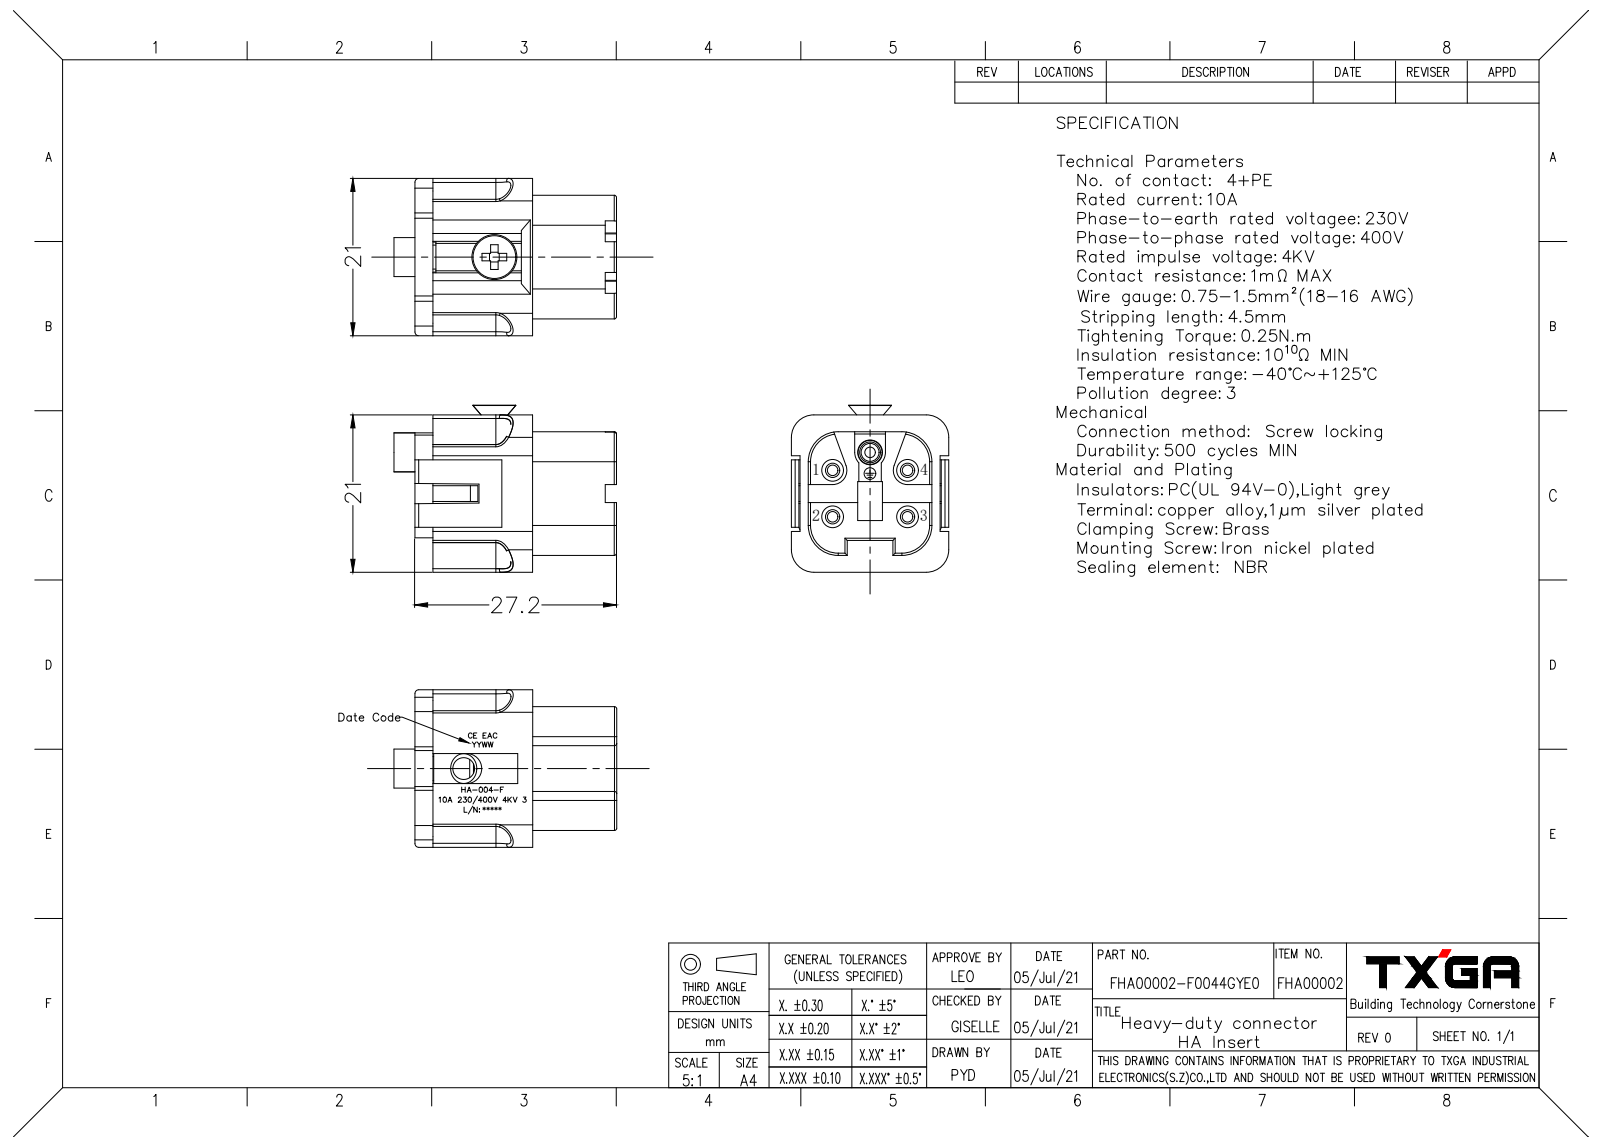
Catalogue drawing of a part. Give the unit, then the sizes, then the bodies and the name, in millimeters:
Units: millimetres
Overall size (bounding box): 29.7 × 22.3 × 21
Round holes (diameter × count): ⌀3.3 ×5, ⌀3.5 ×5, ⌀1.9 ×4, ⌀4.7 ×4, ⌀1.4 ×3, ⌀1.7 ×3, ⌀2.5 ×3, ⌀2.8 ×3, ⌀2.25 ×2, ⌀2.9 ×2, ⌀3 ×1
Round bosses / shafts (diameter × count): ⌀4.5 ×4, ⌀3.2 ×4, ⌀2 ×2, ⌀5.7 ×1, ⌀5.2 ×1, ⌀2.6 ×1
Partial cylindrical surfaces — rounded edges, fillets, slot ends (radius × count): R0.15 ×40, R0.2 ×16, R0.3 ×15, R2 ×7, R1.6 ×6, R1.55 ×5, R0.5 ×4, R3 ×4
Main face-to-face distances: 18.75, 4, 2.25, 1.15, 19.85, 11, 9.9, 6.25, 2.4, 13.3
Hole centre spacings: 3.98, 12.88, 5.55, 6.2, 9.3, 9.95, 10, 11.77
Volume: 6 420 mm³ · Surface area: 7 601 mm²
Bodies: 1 solid, 713 faces (400 planar, 200 cylindrical, 113 other)
Part name (STEP PRODUCT): FHA00002-F0044GYE0 HA-004-F
STEP written by: SolidWorks 2021 (CONFIG_CONTROL_DESIGN)
